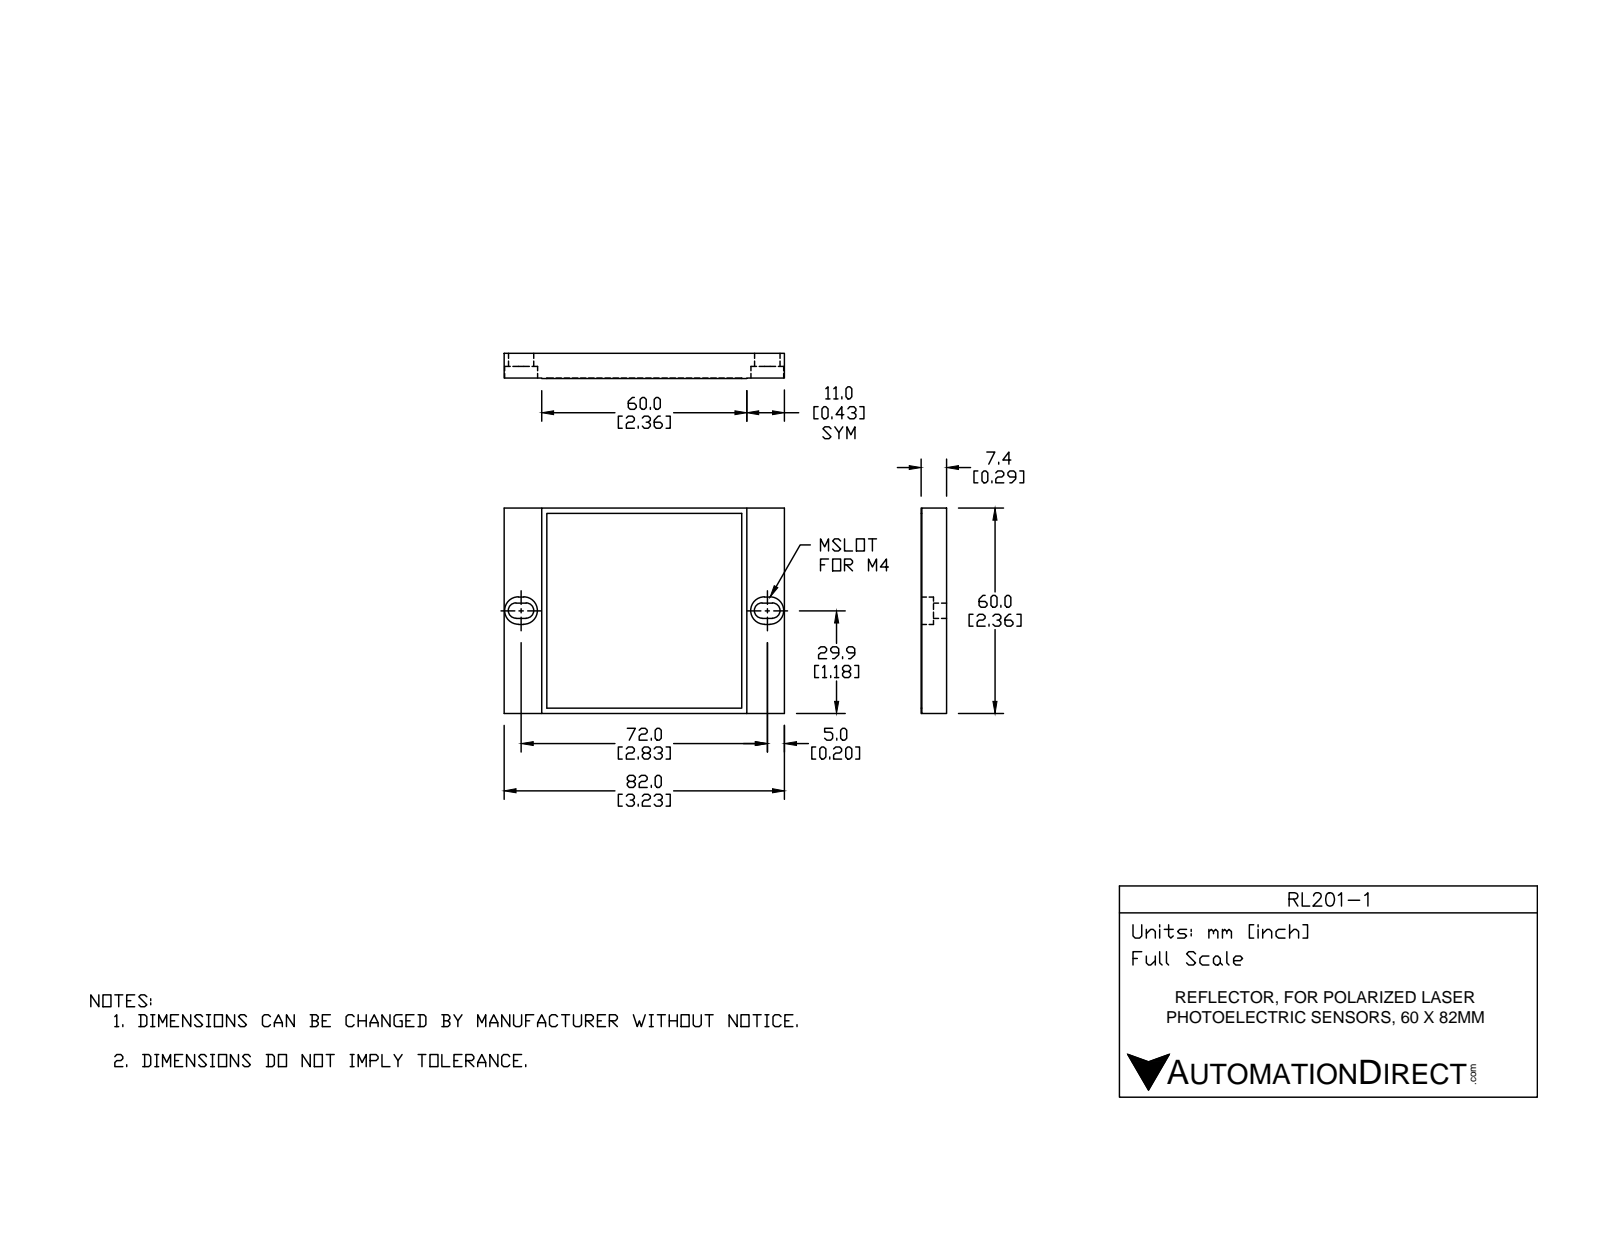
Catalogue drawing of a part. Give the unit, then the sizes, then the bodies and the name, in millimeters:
Units: millimetres
Overall size (bounding box): 82 × 60 × 7.4
Partial cylindrical surfaces — rounded edges, fillets, slot ends (radius × count): R2.2 ×4, R4 ×4
Main face-to-face distances: 7.2, 60, 82, 7.4, 3.8, 3.4, 3.6, 27.8, 32.2, 1.5
Volume: 34 860 mm³ · Surface area: 12 210 mm²
Bodies: 1 solid, 37 faces (25 planar, 12 cylindrical, 0 other)
Part name (STEP PRODUCT): RL-201-1
STEP written by: SolidWorks 2017 (AUTOMOTIVE_DESIGN)
